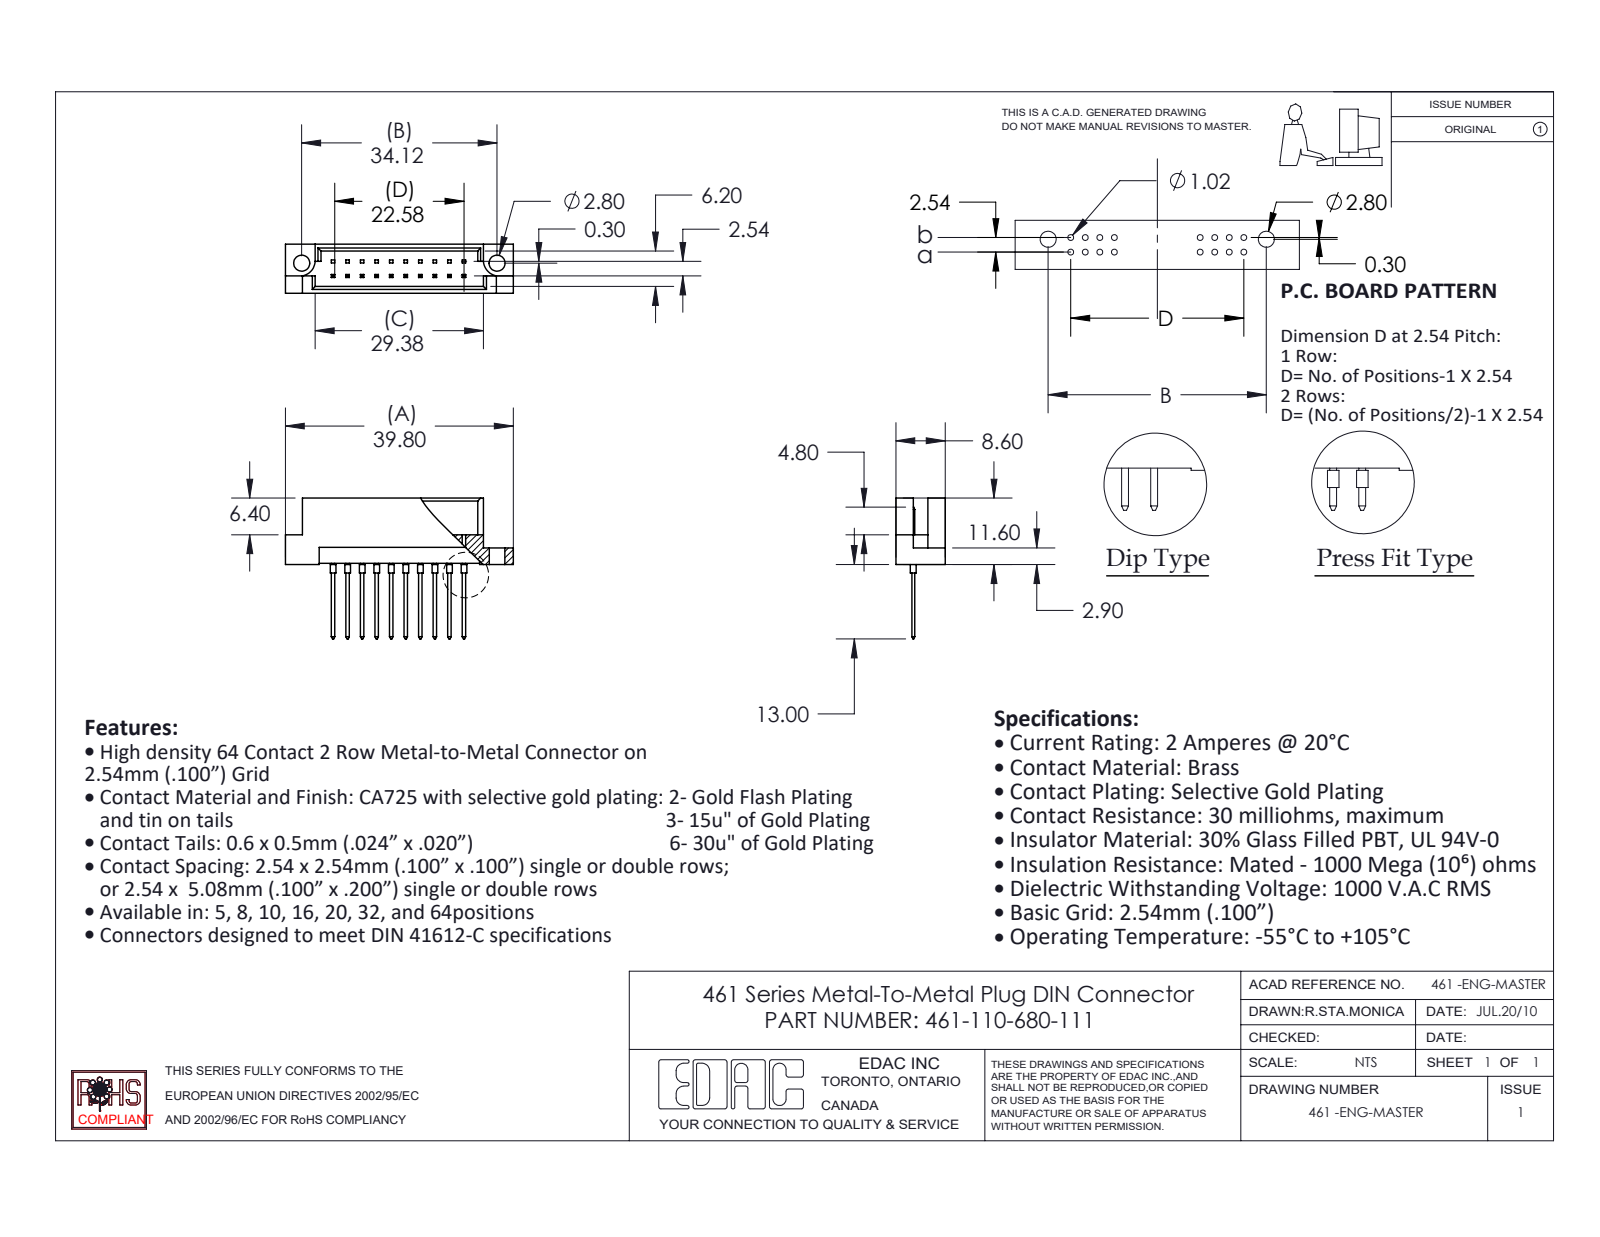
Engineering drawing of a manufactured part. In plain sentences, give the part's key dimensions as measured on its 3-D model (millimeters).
The part is named "461-290_80; 461-110-680-111; 461 Part_20". Its 3-D file was written by "SolidWorks 2020 (CONFIG_CONTROL_DESIGN)". It is 11 solids with 348 faces: 322 planar, 26 cylindrical and 0 other. Overall it measures 39.8 by 24.6 by 8.6 millimeters. Its volume is 1 980 cubic millimeters and its surface area 2 864 square millimeters. Round holes: 2 of diameter 2.8. Round bosses or shafts: 10 of diameter 1. Partial cylindrical surfaces (rounded edges, fillets, slot ends): 2 of radius 2.8. The main face-to-face distances are 1.2, 7.4, 8.6, 2.54, 6.2, 3.28, 5.32, 2.08, 4.12, 2.78. The hole center spacings are 34.12.
